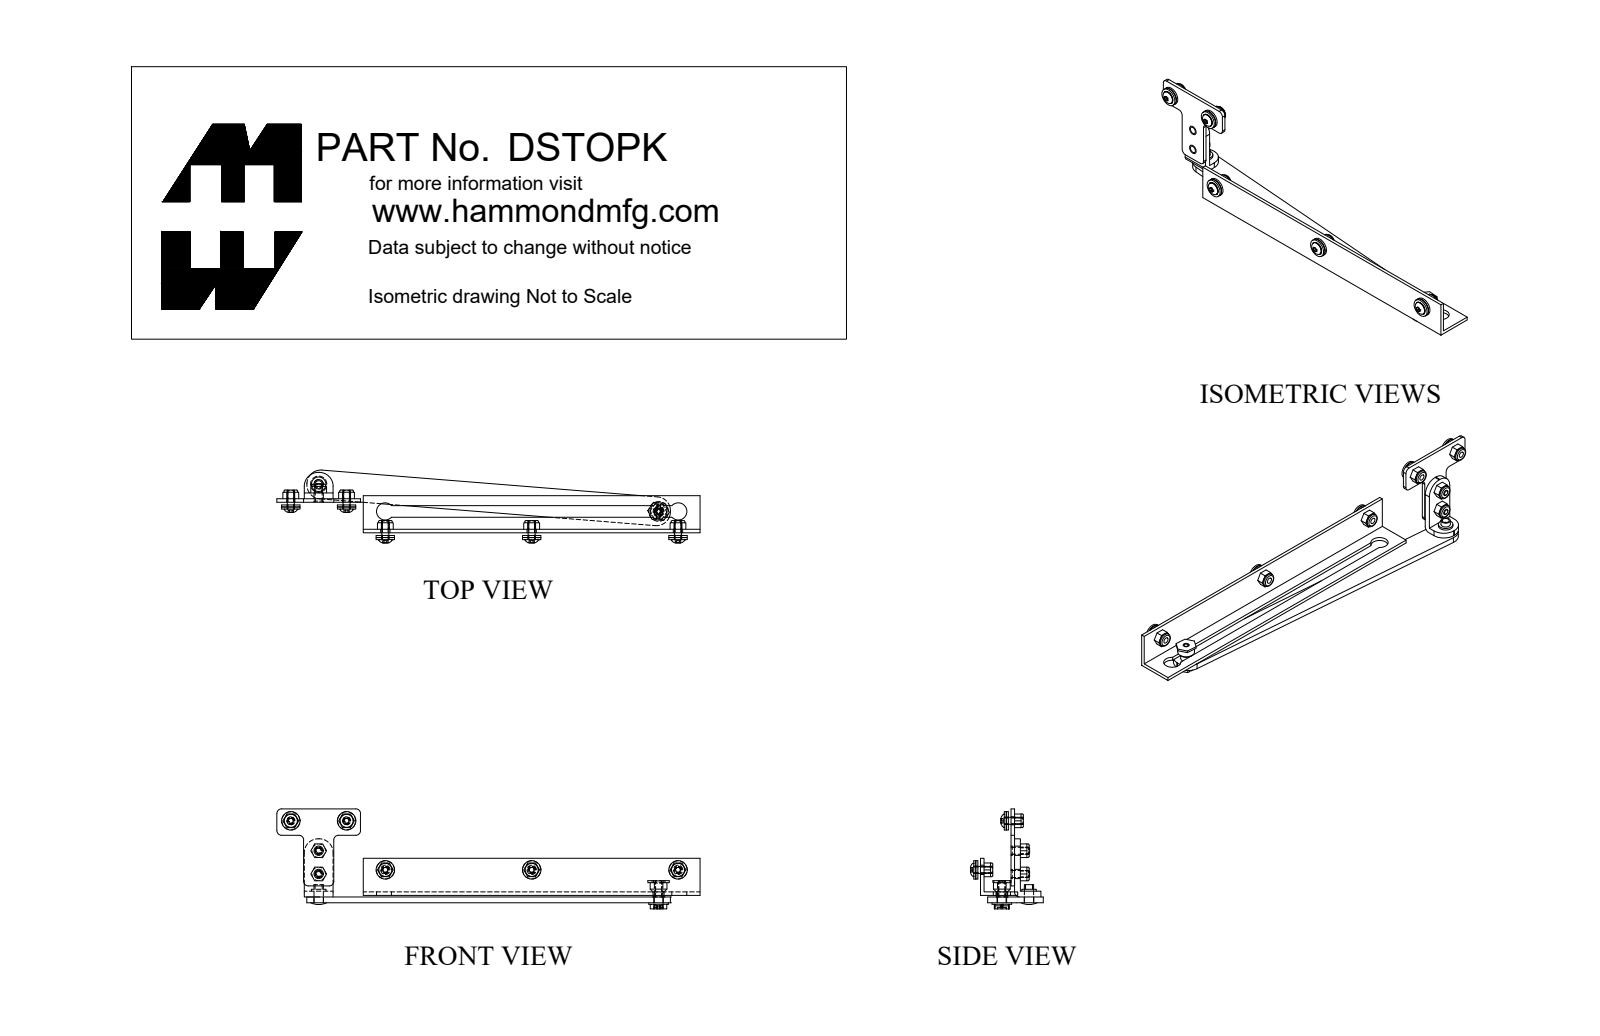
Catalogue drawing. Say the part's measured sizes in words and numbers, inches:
The part is named "DSTOPK_Default". Its 3-D file was written by "SolidWorks 2018 (CONFIG_CONTROL_DESIGN)". It is 27 solids with 459 faces: 237 planar, 169 cylindrical and 53 other. Overall it measures 11.389 by 2.689 by 1.958 inches. Its volume is 3.476 cubic inches and its surface area 74.89 square inches. Round holes: 7 of diameter 0.156, 6 of diameter 0.25, 5 of diameter 0.197, 2 of diameter 0.191, 2 of diameter 0.218, 2 of diameter 0.256, 1 of diameter 0.159, 1 of diameter 0.19. Round bosses or shafts: 5 of diameter 0.494, 5 of diameter 0.488, 5 of diameter 0.352, 5 of diameter 0.19, 4 of diameter 0.365, 3 of diameter 0.365, 2 of diameter 0.188, 1 of diameter 0.528. Partial cylindrical surfaces (rounded edges, fillets, slot ends): 10 of radius 0.125, 8 of radius 0.375, 6 of radius 0.007, 2 of radius 0.231. The main face-to-face distances are 0.095, 0.157, 0.822, 0.198, 0.041, 0.293, 0.135, 0.917, 0.727, 1. The hole center spacings are 1.1, 1.615, 0.625, 1.5, 1.682, 1.798, 1.867, 2.866.
